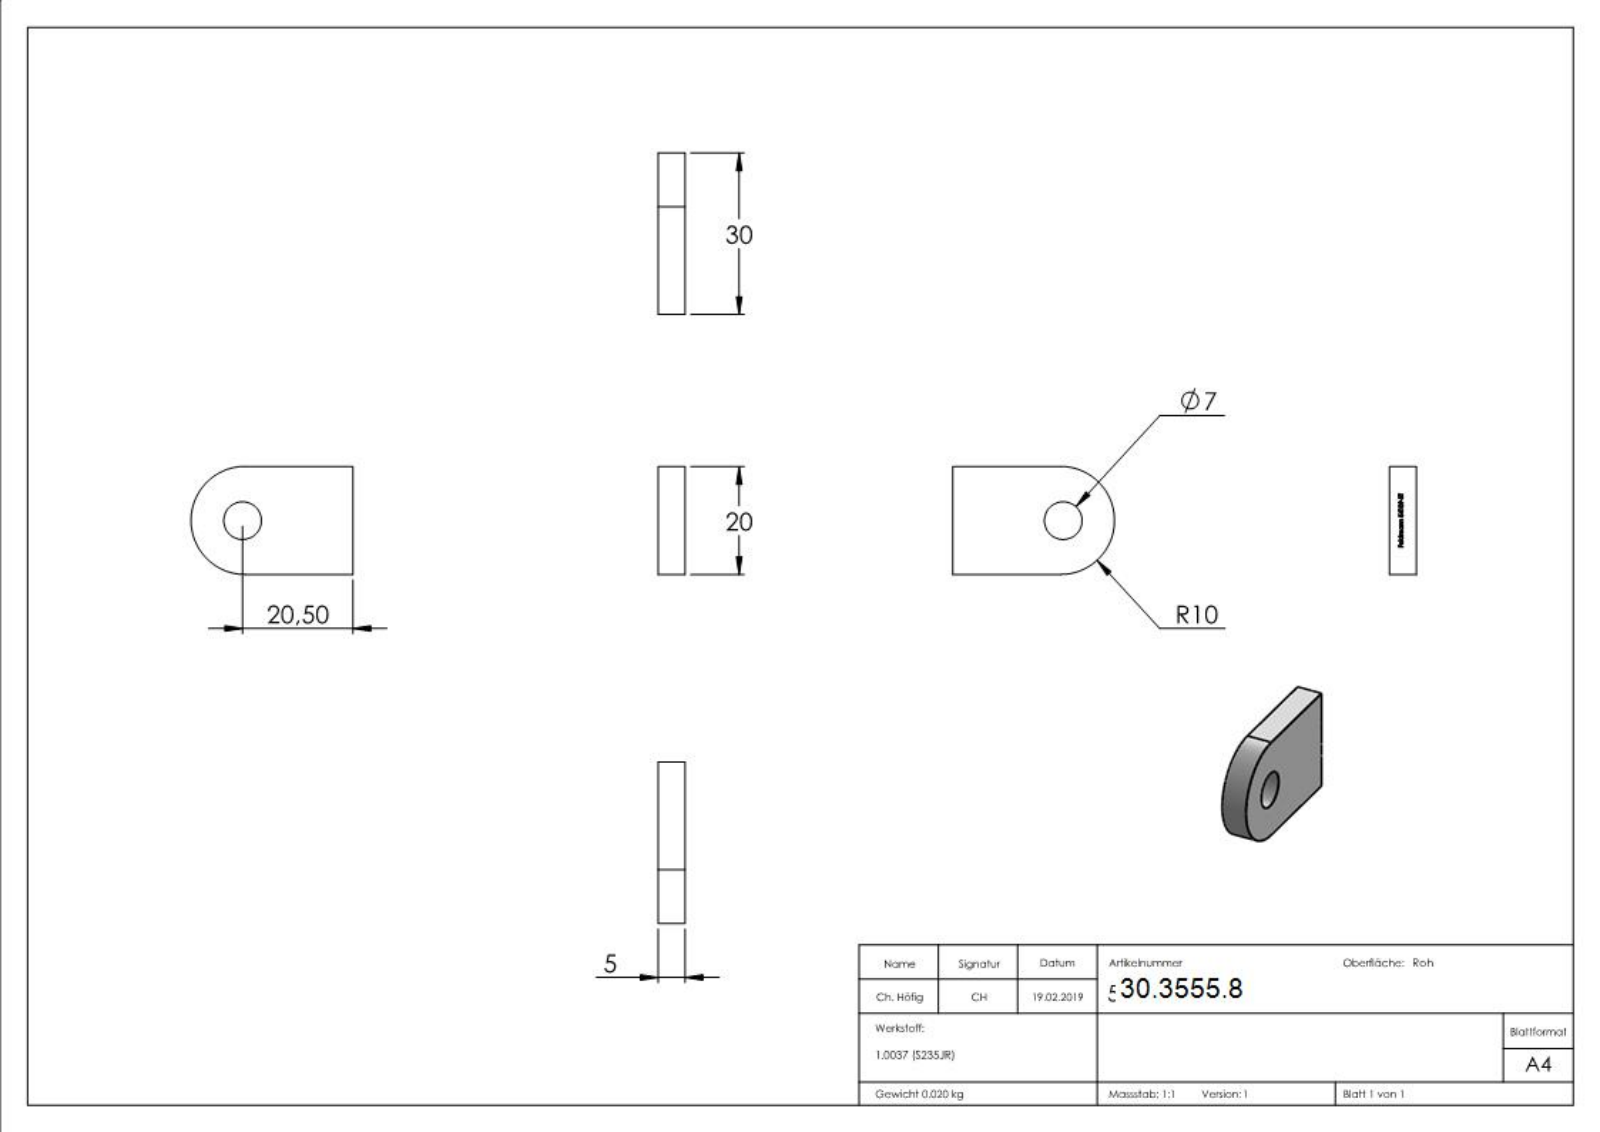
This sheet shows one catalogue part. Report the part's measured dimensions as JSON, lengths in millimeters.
{"part_name": "54109-ST", "step_written_by": "SolidWorks 2015 (CONFIG_CONTROL_DESIGN)", "units": "millimeters", "bodies": {"solids": 1, "faces": 216, "planar": 123, "cylindrical": 4, "other": 89}, "overall_size": [30, 20, 5], "volume_mm3": 2593, "surface_area_mm2": 1609, "round_holes": [[7, 1]], "partial_cylinders_radius": [[10, 1]], "face_to_face_distances": [5, 20, 2.5, 1.71, 3.29, 1.79, 3.21, 5.83, 1.21, 8.49]}
